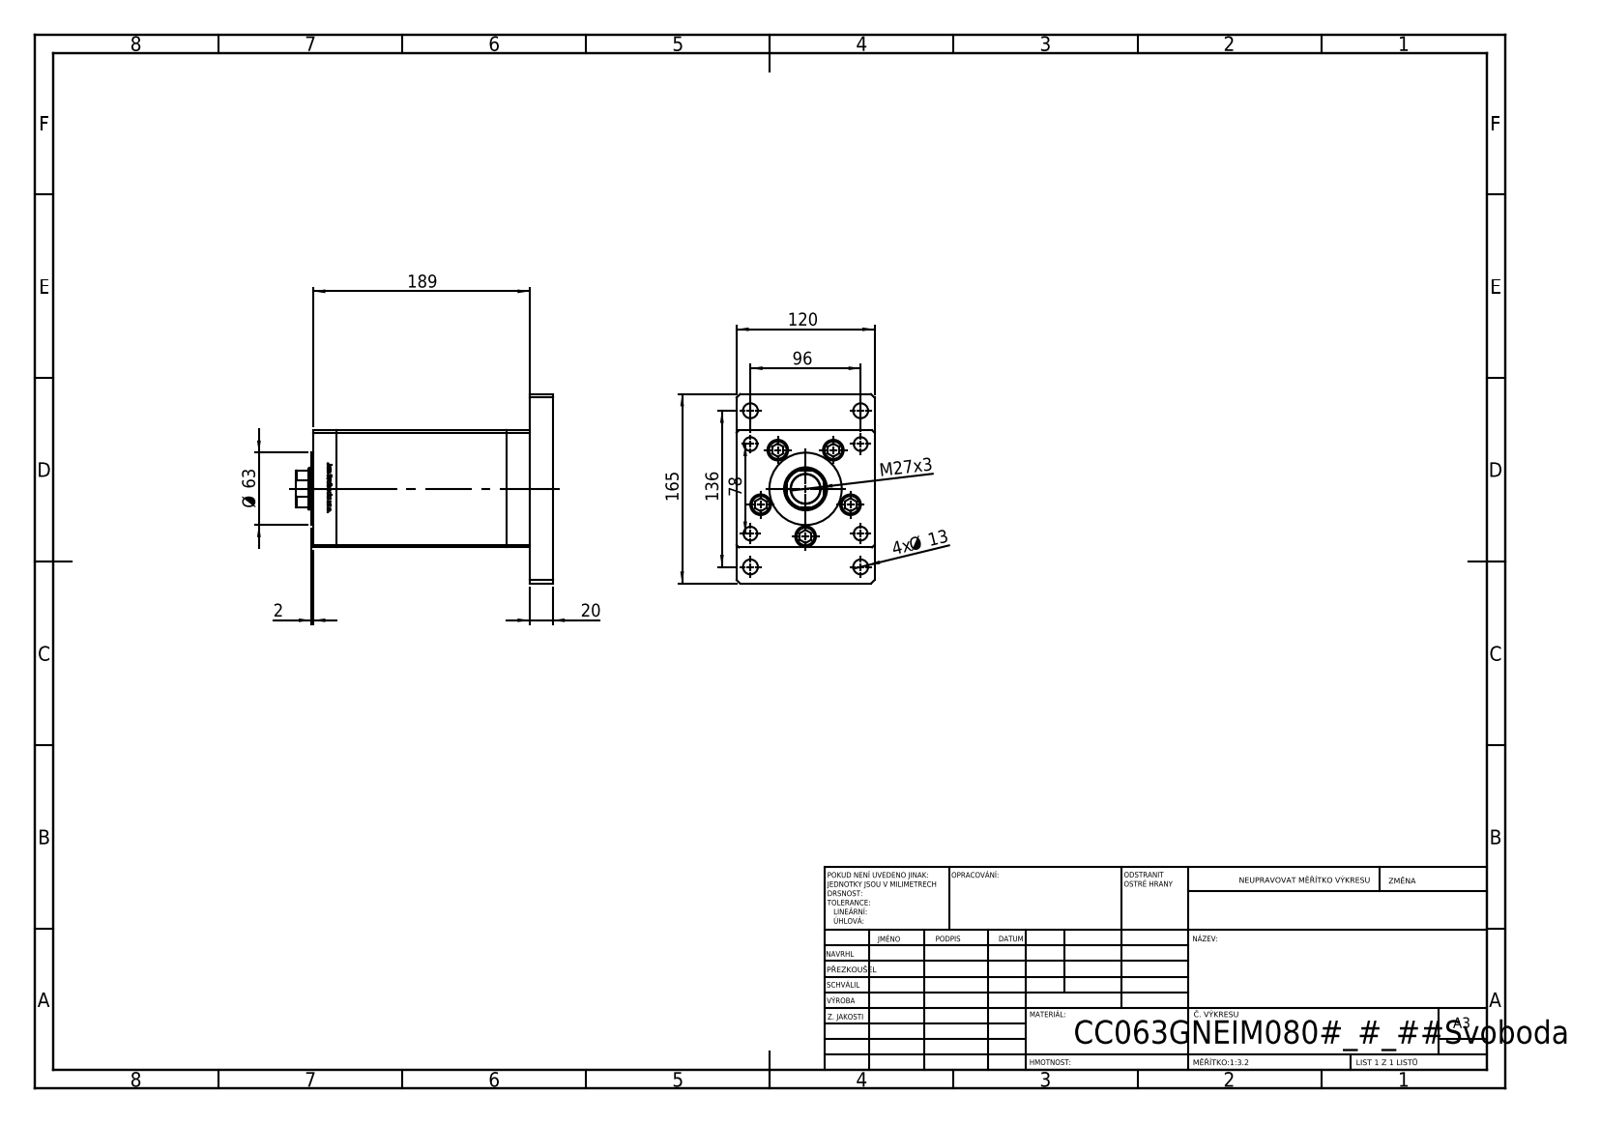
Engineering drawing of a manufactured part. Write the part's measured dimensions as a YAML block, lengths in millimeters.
part_name: "ALLEN BOLT; V220C_FRONT_G; V220C_VC_G; V220C_G_MIDDLE (+2 more)"
step_written_by: "SolidWorks 2019 (CONFIG_CONTROL_DESIGN)"
units: millimeters
bodies: {solids: 19, faces: 1313, planar: 518, cylindrical: 189, other: 606}
overall_size: [223.5, 165, 120]
volume: 2394000
surface_area: 318444
round_holes:
  - {diameter: 12, count: 9}
  - {diameter: 13.5, count: 5}
  - {diameter: 18, count: 5}
  - {diameter: 13, count: 4}
  - {diameter: 17, count: 4}
  - {diameter: 2, count: 2}
  - {diameter: 13.16, count: 2}
  - {diameter: 25.5, count: 1}
  - {diameter: 36, count: 1}
  - {diameter: 37.5, count: 1}
  - {diameter: 83, count: 1}
round_bosses_or_shafts:
  - {diameter: 8, count: 9}
  - {diameter: 17, count: 5}
  - {diameter: 63, count: 1}
partial_cylinders:
  - {radius: 0.93, count: 2}
  - {radius: 17.5, count: 1}
face_to_face_distances: [20, 168.5, 120, 188.5, 102, 148.5, 40, 2, 186.5, 18]
hole_center_spacings: [41.5, 29, 61.85, 83.23, 96, 100.28, 107, 143.75]
